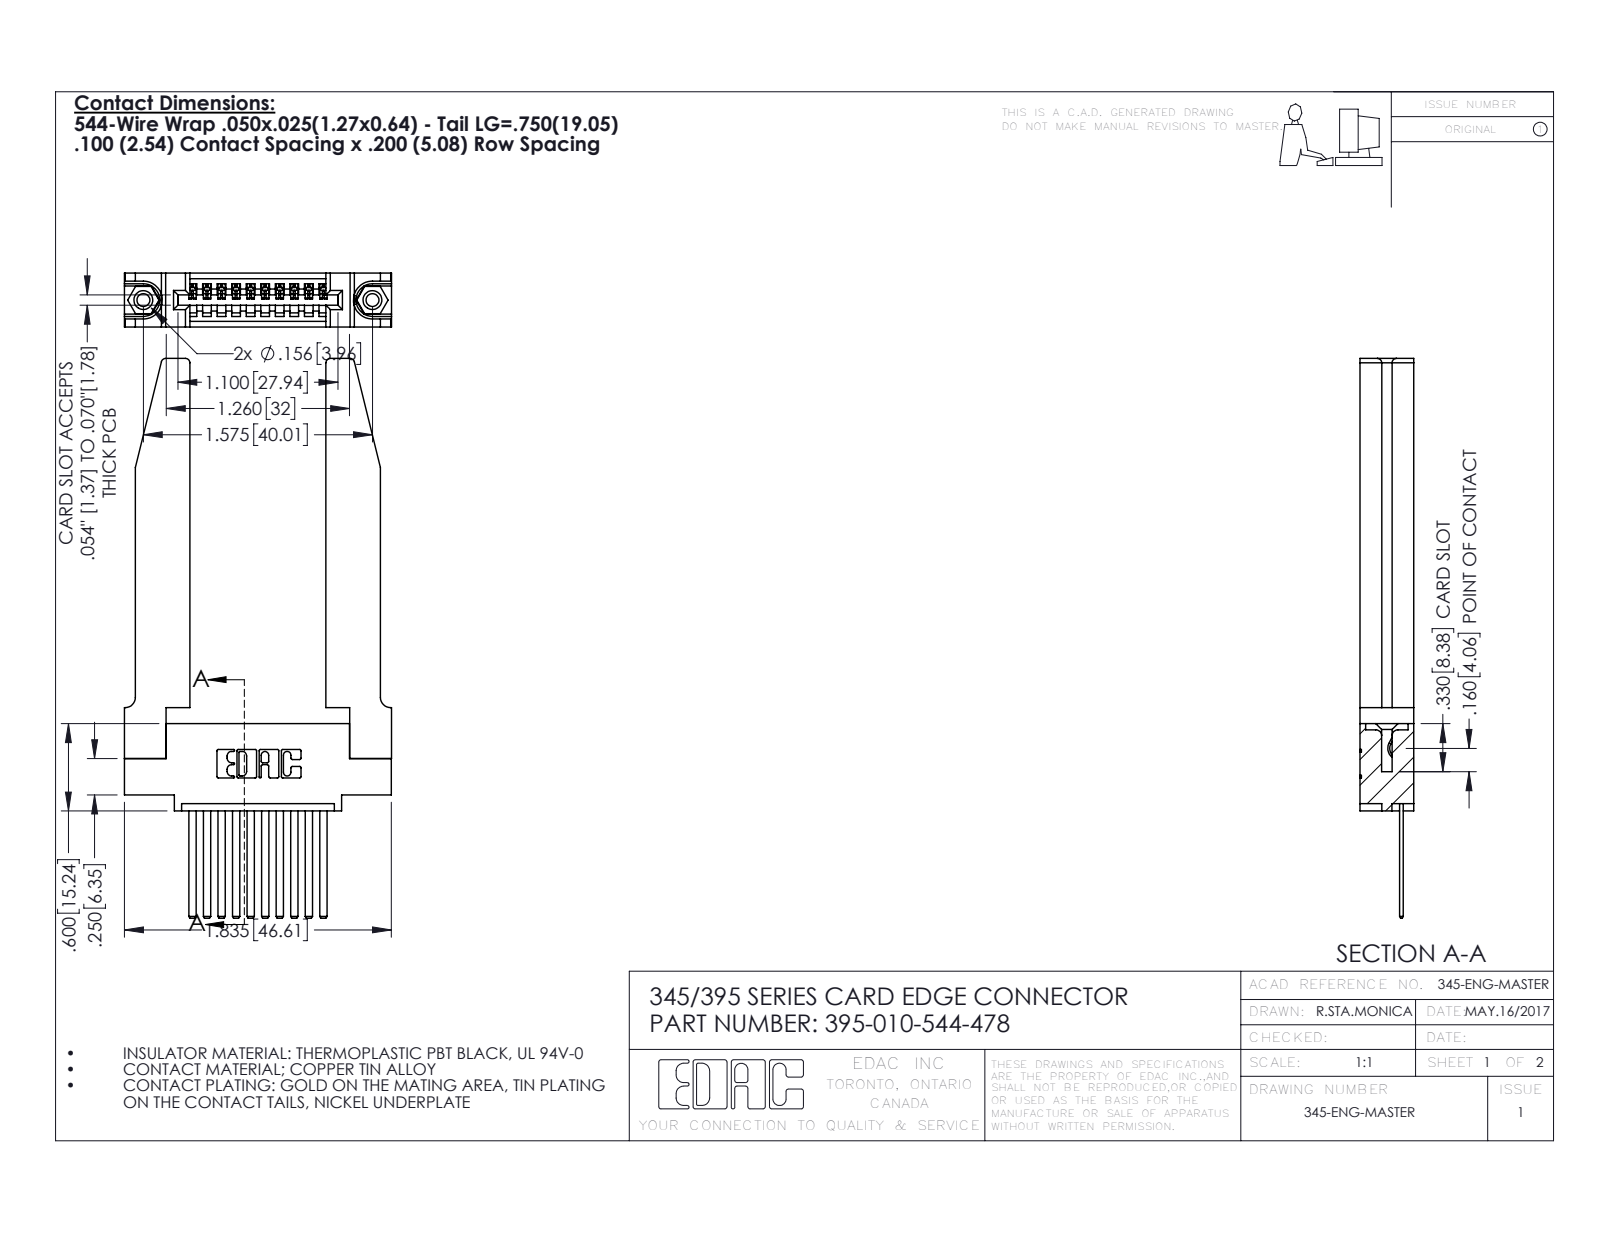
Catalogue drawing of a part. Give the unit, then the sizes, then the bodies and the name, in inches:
Units: inches
Overall size (bounding box): 3.847 × 1.836 × 0.37
Round holes (diameter × count): ⌀0.089 ×2, ⌀0.125 ×2, ⌀0.156 ×2, ⌀0.064 ×1
Round bosses / shafts (diameter × count): ⌀0.155 ×2
Partial cylindrical surfaces — rounded edges, fillets, slot ends (radius × count): R0.01 ×22, R0.006 ×20, R0.03 ×8, R0.007 ×6, R0.031 ×6, R0.026 ×3, R0.031 ×2, R0.04 ×2
Main face-to-face distances: 0.37, 0.072, 0.298, 0.15, 0.148, 0.098, 0.272, 0.025, 0.22, 0.077
Hole centre spacings: 0.27, 1.344, 1.575
Volume: 0.731 in³ · Surface area: 19.27 in²
Bodies: 15 solids, 884 faces (586 planar, 246 cylindrical, 52 other)
Part name (STEP PRODUCT): 345-250-001_345-250-001-102; 395-010-544-478; 345-220-078_345-220-078; 345-292-001_345-293-144 (+1 more)
STEP written by: SolidWorks 2016 (CONFIG_CONTROL_DESIGN)
